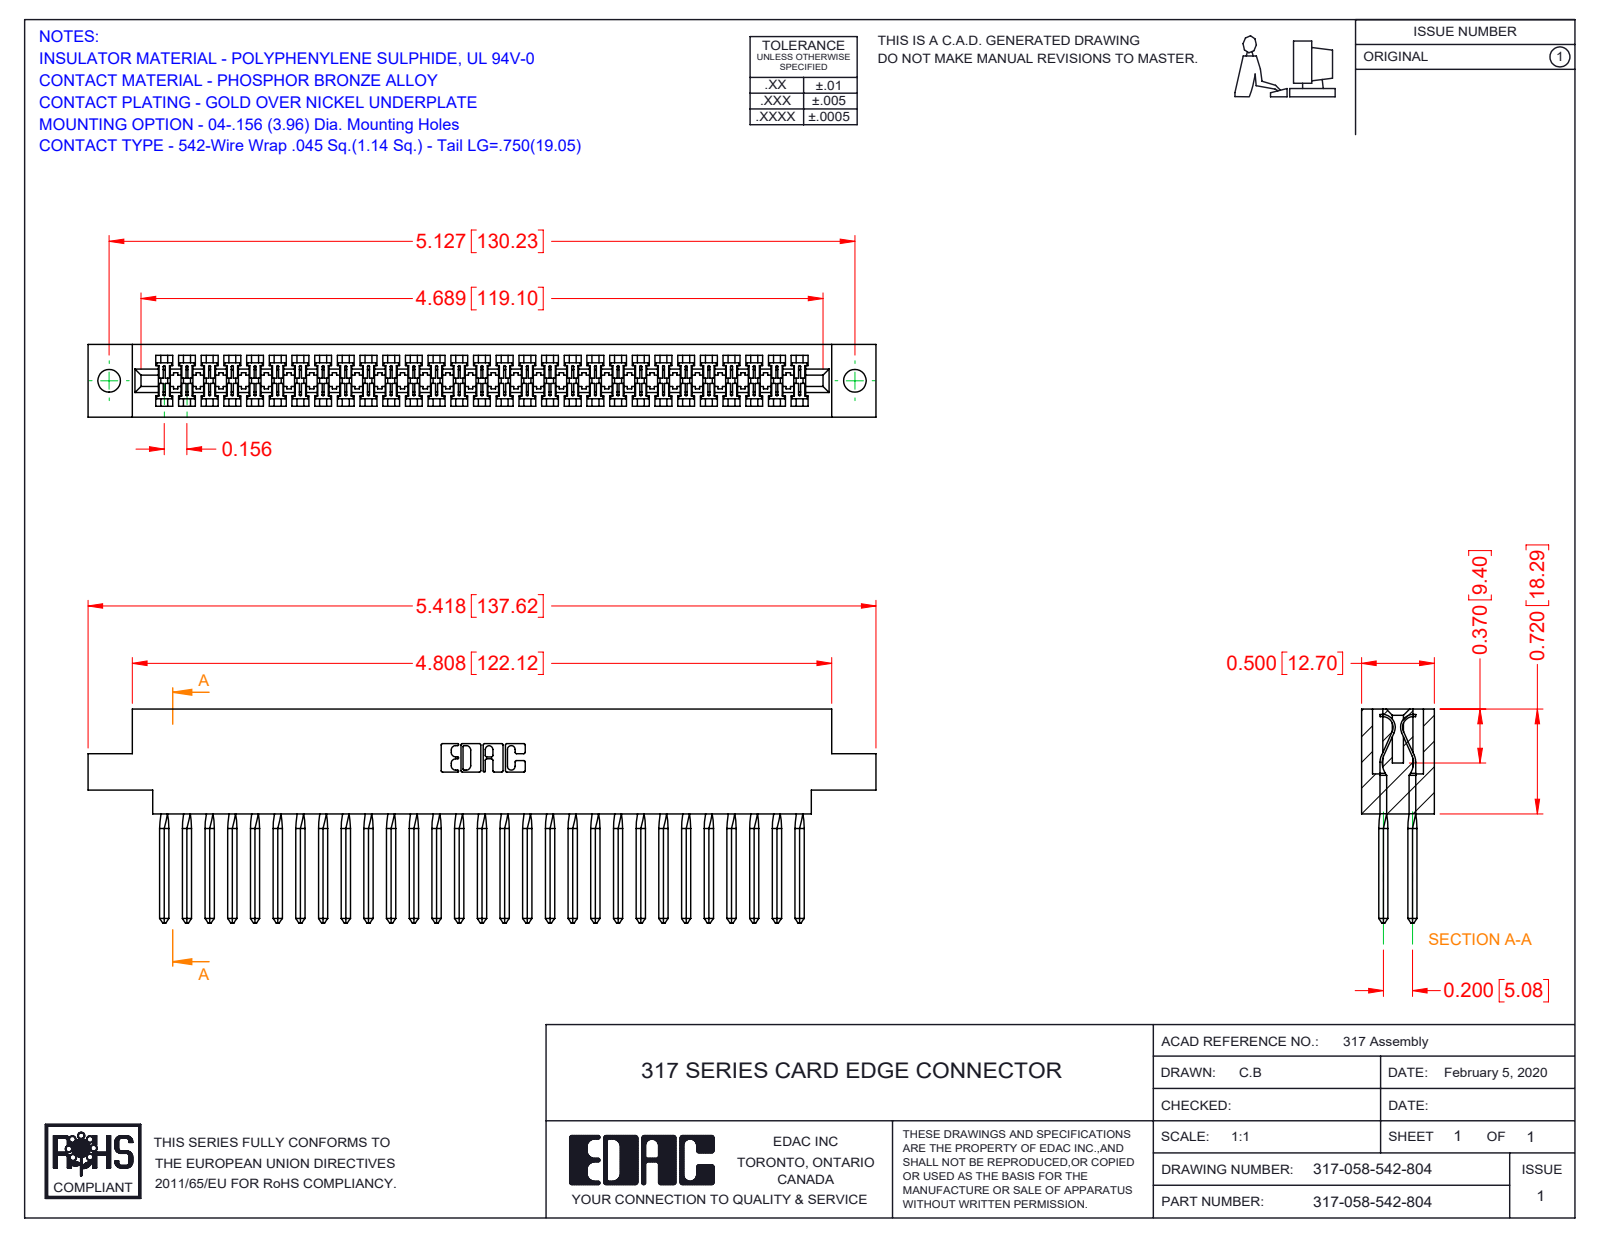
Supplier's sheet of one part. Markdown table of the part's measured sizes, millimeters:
| quantity | value |
| --- | --- |
| part name | 317 Part_.156 Dia - TH; 317-058-542-804; 317-290-003_542 |
| STEP written by | SolidWorks 2016 (CONFIG_CONTROL_DESIGN) |
| units | millimeters |
| bodies | 59 solids, 3408 faces (2726 planar, 450 cylindrical, 232 other) |
| overall size | 137.6 × 37.3 × 12.7 |
| volume | 22 040 mm³ |
| surface area | 30 050 mm² |
| round holes (diameter × count) | 4 × 2 |
| partial cylindrical surfaces (radius × count) | 0.2 × 116, 0.3 × 22, 0.2 × 6, 0.8 × 6, 0.7 × 3, 1.9 × 2, 2.3 × 2, 2.5 × 2 |
| main face-to-face distances | 12.7, 1.9, 10.8, 8.9, 5.1, 2.8, 1.2, 2.9, 3.3, 9.4 |
| hole center spacings | 130.2 |
